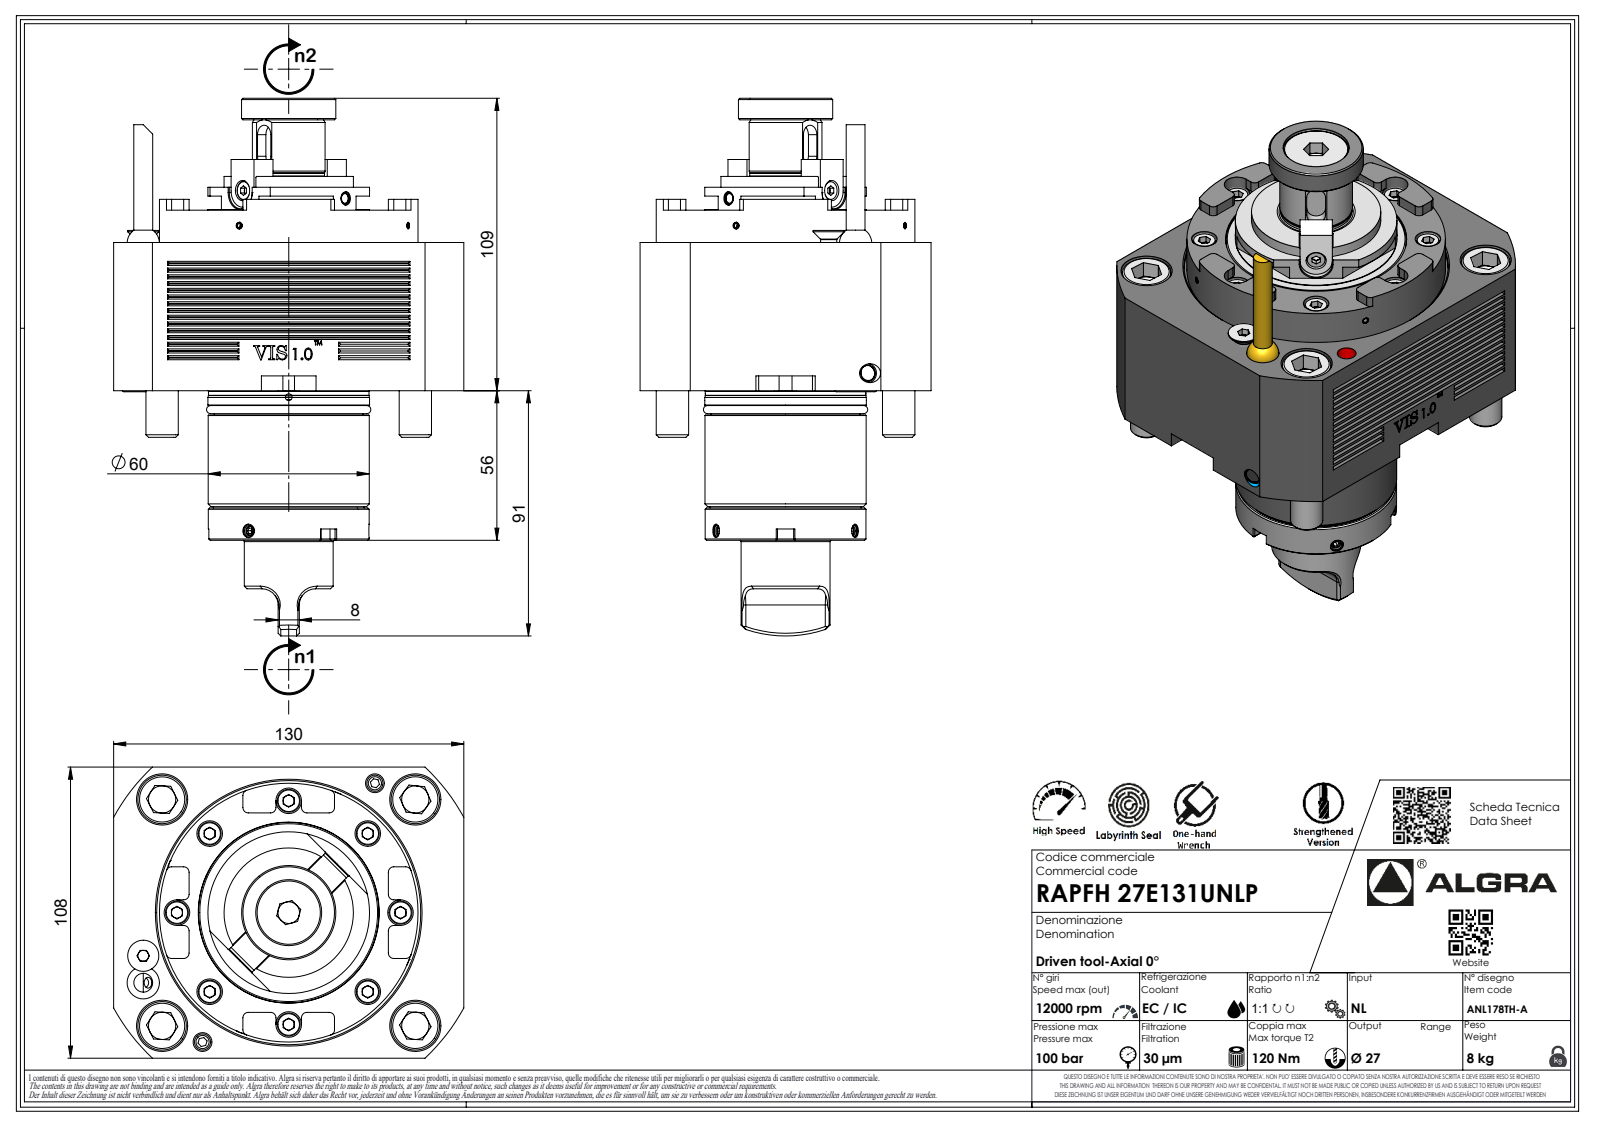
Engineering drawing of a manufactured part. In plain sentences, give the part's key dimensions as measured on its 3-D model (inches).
The part is named "RAPFH27E131UNLP". Its 3-D file was written by "SolidWorks 2023 (AUTOMOTIVE_DESIGN)". It is 1 solid with 514 faces: 345 planar, 90 cylindrical and 79 other. Overall it measures 7.854 by 5.118 by 4.252 inches. Its volume is 64.75 cubic inches and its surface area 125.3 square inches. Round holes: 1 of diameter 0.083. Round bosses or shafts: 4 of diameter 0.472, 1 of diameter 3.78, 1 of diameter 2.362, 1 of diameter 1.89, 1 of diameter 1.378, 1 of diameter 1.299, 1 of diameter 1.063, 1 of diameter 0.251. Partial cylindrical surfaces (rounded edges, fillets, slot ends): 24 of radius 0.079, 10 of radius 0.236, 8 of radius 0.315, 7 of radius 0.013, 7 of radius 0.02, 7 of radius 0.146, 4 of radius 0.187, 1 of radius 0.008. The main face-to-face distances are 2.165, 4.252, 0.472, 5.118, 2.638, 2.185, 4.35, 4.823, 0.157, 0.335.
